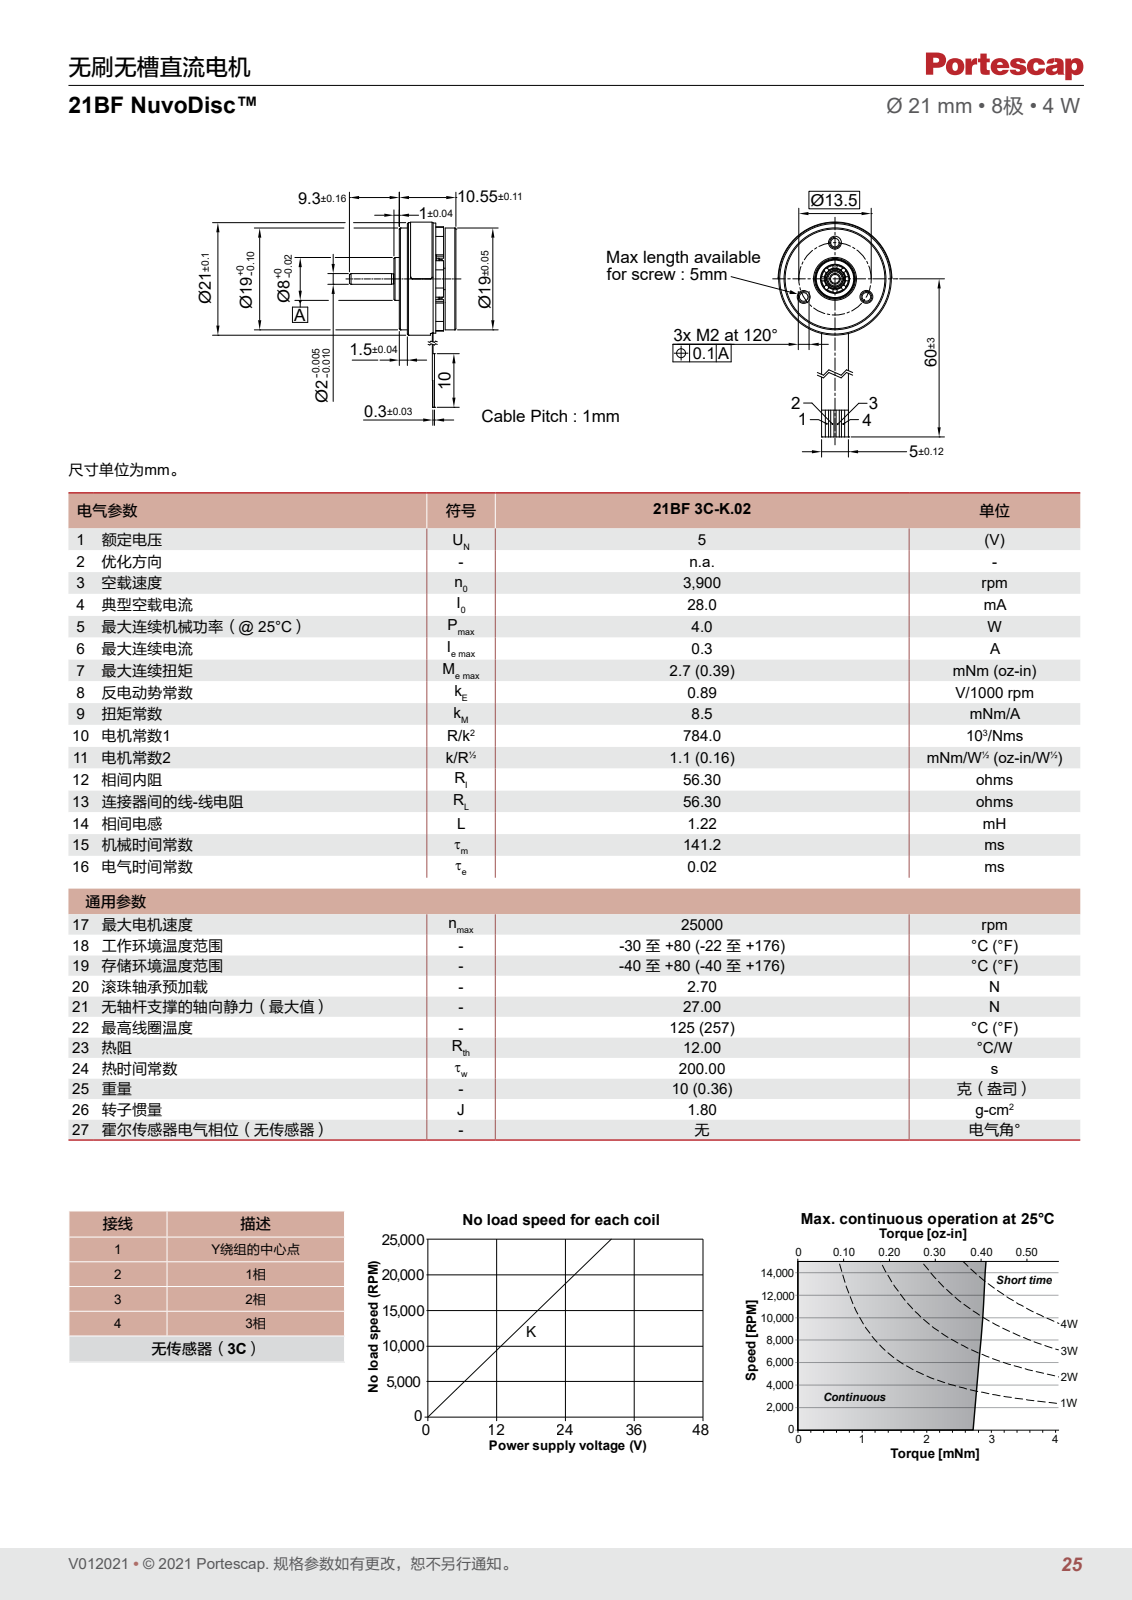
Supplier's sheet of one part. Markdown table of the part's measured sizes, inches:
| quantity | value |
| --- | --- |
| part name | 21BF_NUVODISC_ASM |
| STEP written by | PRO/ENGINEER BY PARAMETRIC TECHNOLOGY CORPORATION, 2014310 (CONFIG_CONTROL_DESIGN) |
| units | inches |
| bodies | 1 solid, 214 faces (94 planar, 56 cylindrical, 64 other) |
| overall size | 2.784 × 0.835 × 0.781 |
| volume | 0.209 in³ |
| surface area | 3.368 in² |
| round holes (diameter × count) | 0.063 × 3, 0.118 × 1, 0.22 × 1, 0.276 × 1 |
| round bosses / shafts (diameter × count) | 0.827 × 1, 0.821 × 1, 0.748 × 1, 0.728 × 1, 0.315 × 1, 0.173 × 1, 0.079 × 1, 0.071 × 1 |
| partial cylindrical surfaces (radius × count) | 0.083 × 12, 0.343 × 6, 0.012 × 2, 0.378 × 1, 0.417 × 1 |
| main face-to-face distances | 0.173, 0.243, 0.415, 0.248, 0.168, 0.258, 0.157, 0.091, 0.015, 0.059 |
| hole center spacings | 0.461, 0.266, 0.266 |
